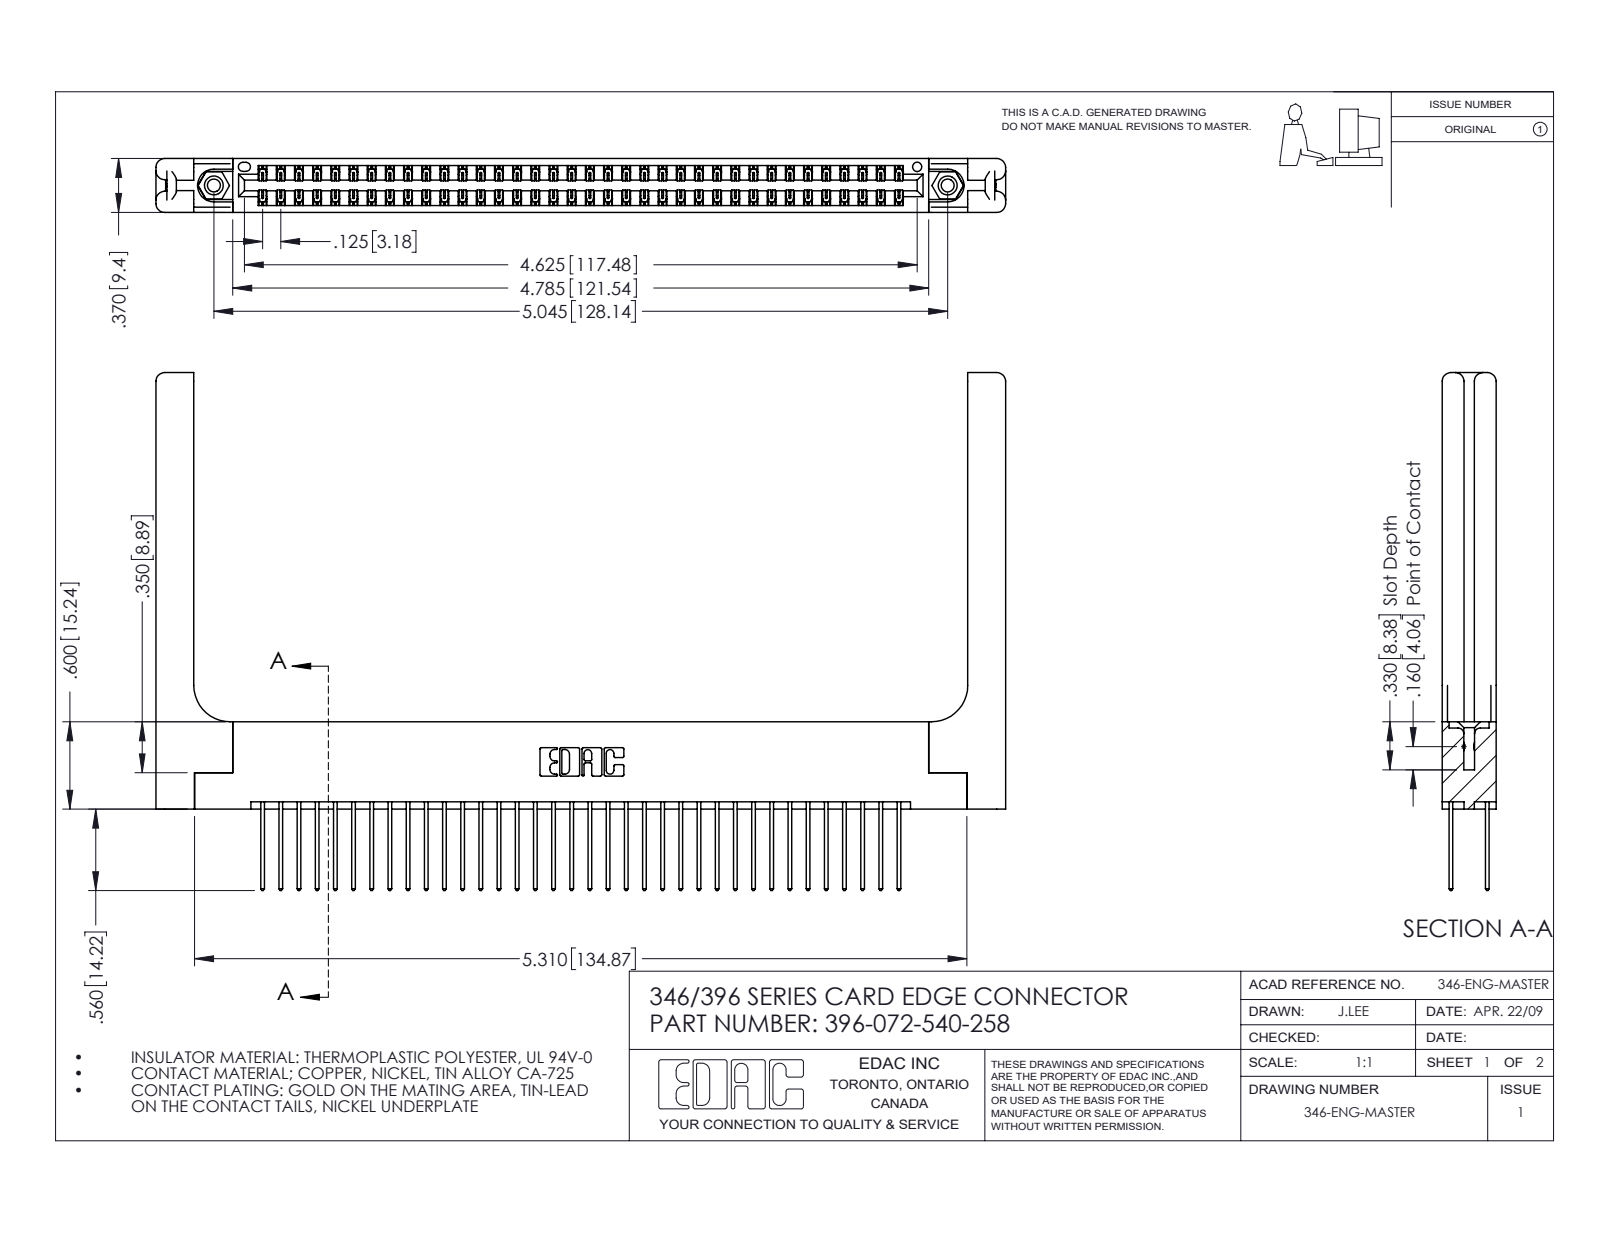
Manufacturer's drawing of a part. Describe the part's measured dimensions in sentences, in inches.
The part is named "345-292-001_345-293-140; 345-250-001_345-250-001-102; 396-072-540-258; 346-220-058_345-220-058 (+1 more)". Its 3-D file was written by "SolidWorks 2016 (CONFIG_CONTROL_DESIGN)". It is 77 solids with 4122 faces: 2744 planar, 1318 cylindrical and 60 other. Overall it measures 5.841 by 3.56 by 0.37 inches. Its volume is 1.354 cubic inches and its surface area 40.87 square inches. Round holes: 2 of diameter 0.089, 2 of diameter 0.125, 2 of diameter 0.156, 1 of diameter 0.064. Round bosses or shafts: 2 of diameter 0.155. Partial cylindrical surfaces (rounded edges, fillets, slot ends): 108 of radius 0.006, 72 of radius 0.01, 22 of radius 0.01, 16 of radius 0.06, 6 of radius 0.007, 6 of radius 0.031, 3 of radius 0.026, 2 of radius 0.014. The main face-to-face distances are 0.048, 0.322, 0.072, 0.37, 0.25, 0.025, 0.298, 0.148, 0.15, 0.275. The hole center spacings are 0.246, 4.836, 5.045.
